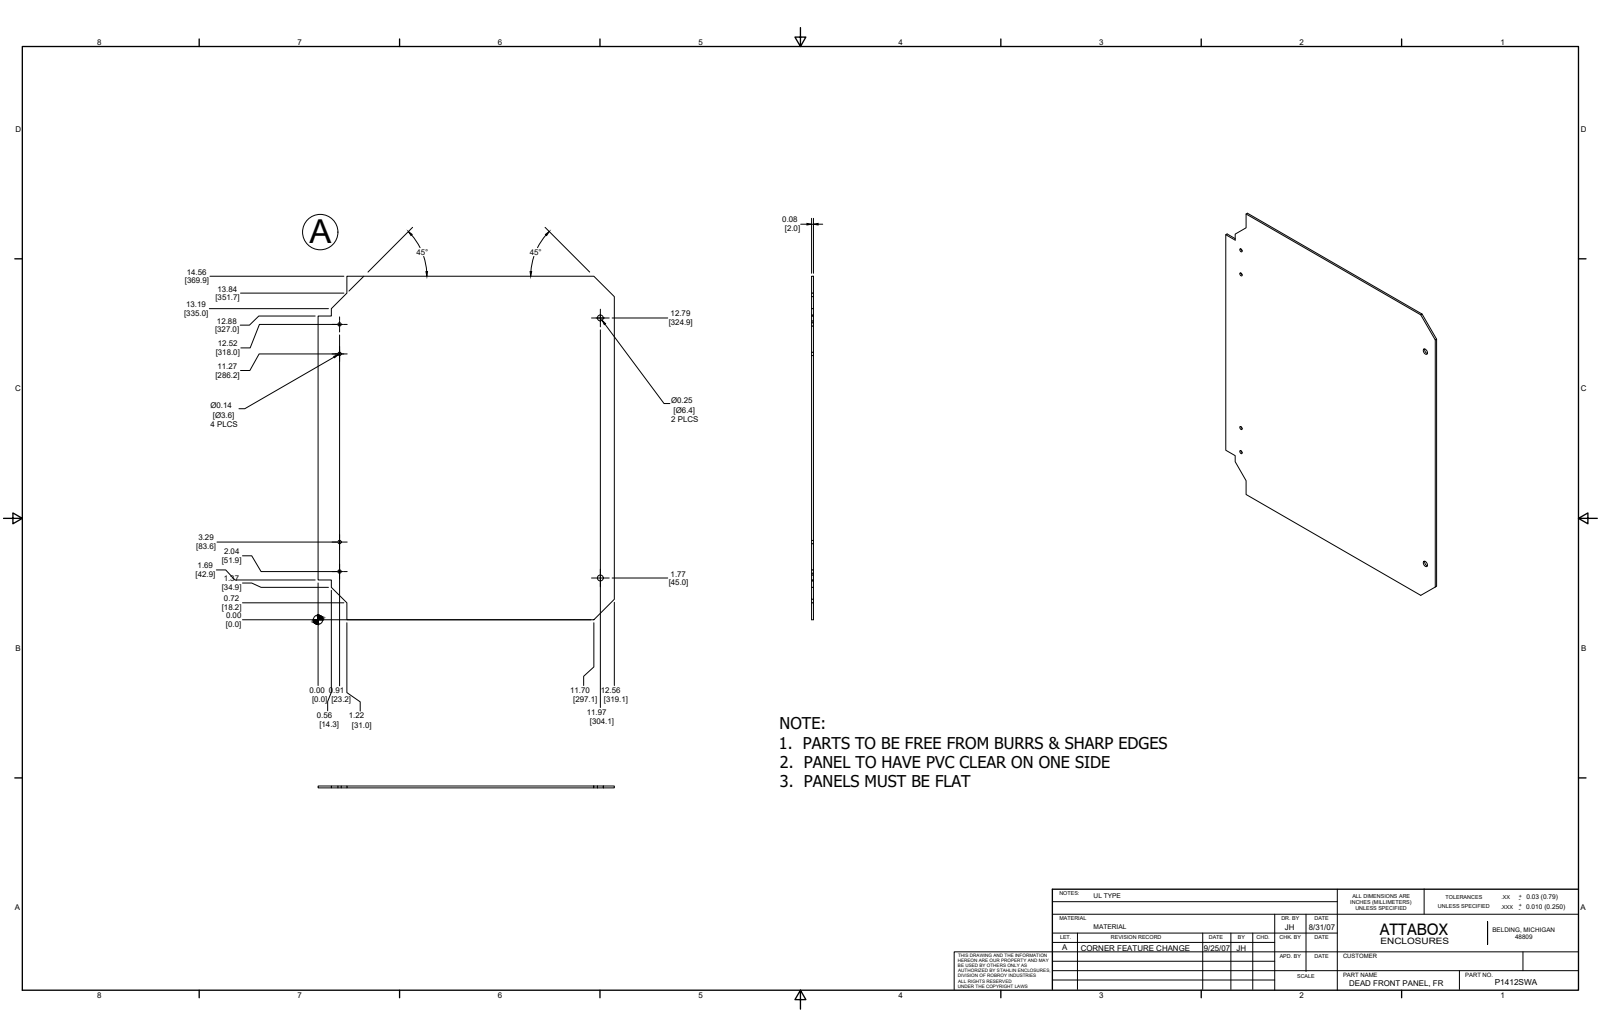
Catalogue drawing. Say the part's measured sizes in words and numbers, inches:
The part is named "P1412SWAL". Its 3-D file was written by "Autodesk Inventor 11 (AUTOMOTIVE_DESIGN)". It is 1 solid with 20 faces: 14 planar, 6 cylindrical and 0 other. Overall it measures 14.563 by 12.563 by 0.08 inches. Its volume is 14.39 cubic inches and its surface area 364.2 square inches. Round holes: 4 of diameter 0.14, 2 of diameter 0.25. The main face-to-face distances are 0.08, 12.562, 14.562, 1.09, 13.472, 11.472, 17.327, 12.383. The hole center spacings are 1.25, 9.226, 11.063, 11.164, 14.578, 15.422, 7.976, 10.476.
